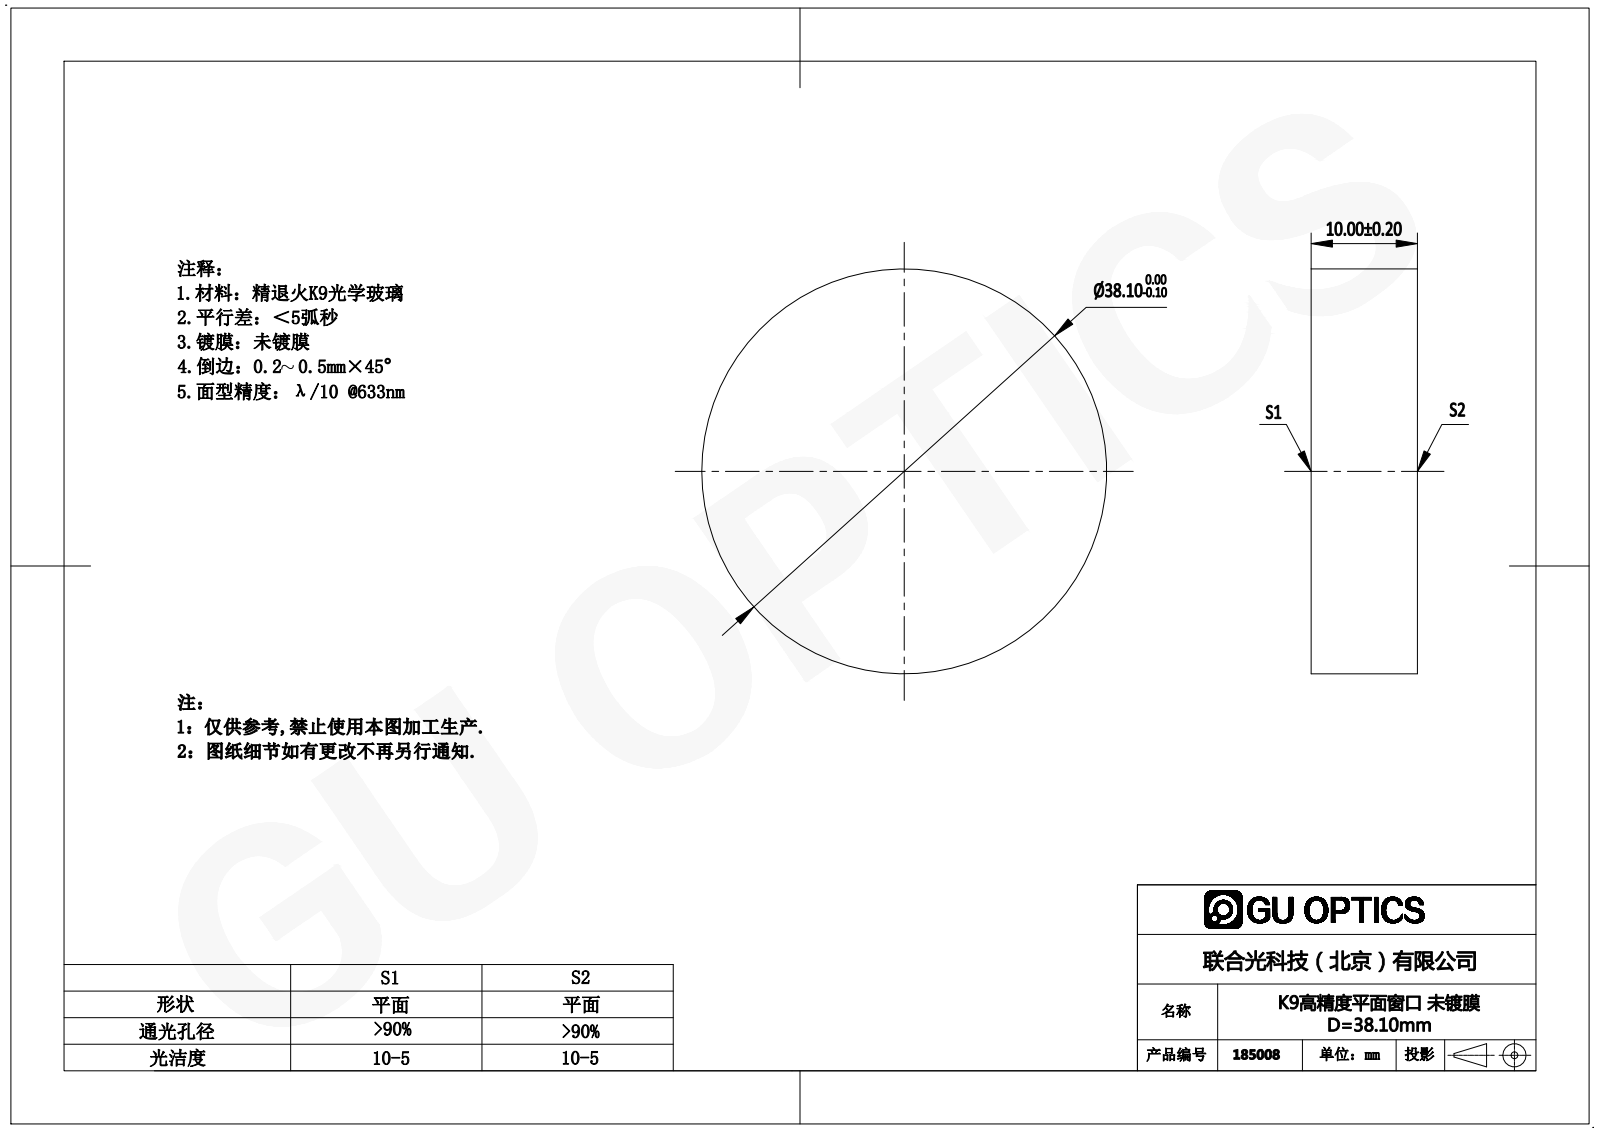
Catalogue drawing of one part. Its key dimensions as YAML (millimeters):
part_name: "185008"
step_written_by: "SolidWorks 2016 (AUTOMOTIVE_DESIGN)"
units: millimeters
bodies: {solids: 1, faces: 4, planar: 2, cylindrical: 2, other: 0}
overall_size: [38.1, 38.1, 10]
volume: 11401
surface_area: 3477
round_bosses_or_shafts:
  - {diameter: 38.1, count: 1}
face_to_face_distances: [10]
